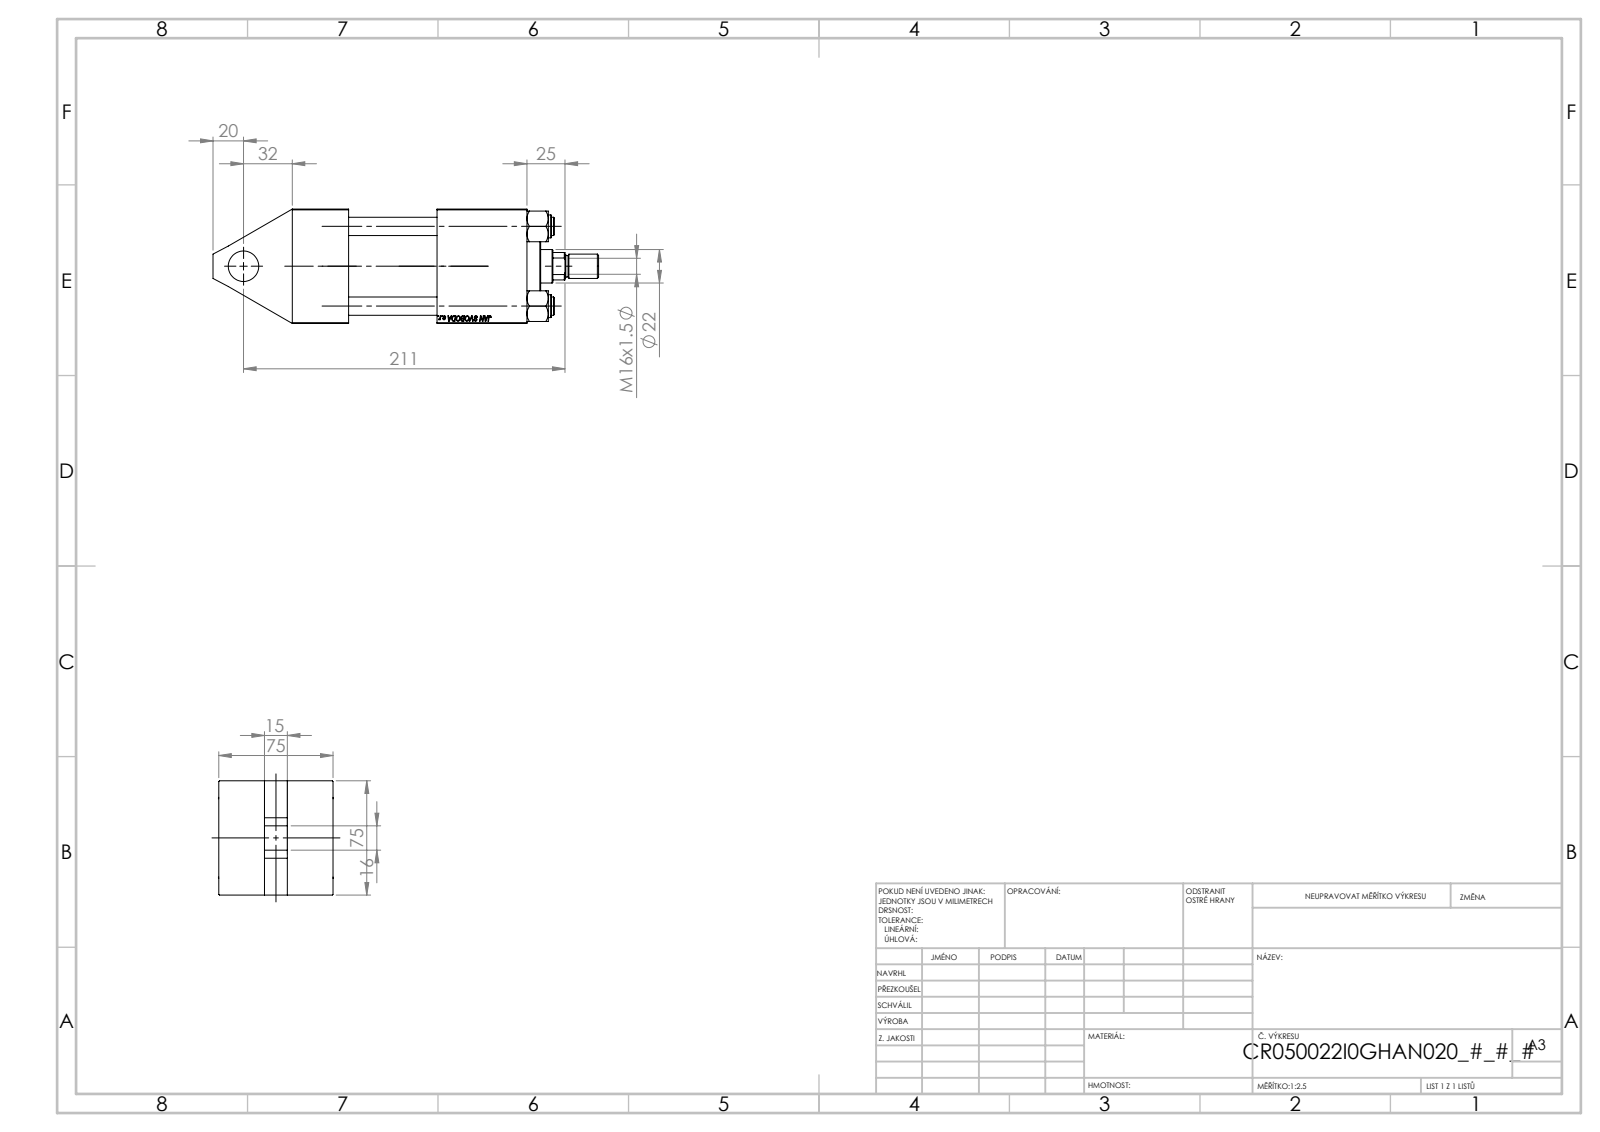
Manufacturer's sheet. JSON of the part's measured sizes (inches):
{"part_name": "V215CR_TYCINKA_I; V215CR_VCP_I; V215_VC_A; V215CR_I_Body (+2 more)", "step_written_by": "SolidWorks 2019 (CONFIG_CONTROL_DESIGN)", "units": "inches", "bodies": {"solids": 12, "faces": 1093, "planar": 506, "cylindrical": 85, "other": 502}, "overall_size": [9.961, 2.974, 2.953], "volume_in3": 42.95, "surface_area_in2": 244.6, "round_holes": [[0.472, 4], [0.276, 2], [0.825, 2], [1.181, 2], [0.413, 1], [0.787, 1], [0.866, 1], [0.984, 1], [1.614, 1], [1.969, 1], [2.087, 1]], "round_bosses_or_shafts": [[0.591, 4], [2.205, 1], [1.339, 1], [0.63, 1], [0.551, 1]], "partial_cylinders_radius": [[0.413, 1]], "face_to_face_distances": [2.953, 4.606, 1.457, 6.063, 1.181, 1.772, 3.74, 2.283, 2.323, 4.933], "hole_center_spacings": [1.456, 2.059, 2.912, 1.988, 3.681, 5.669]}
